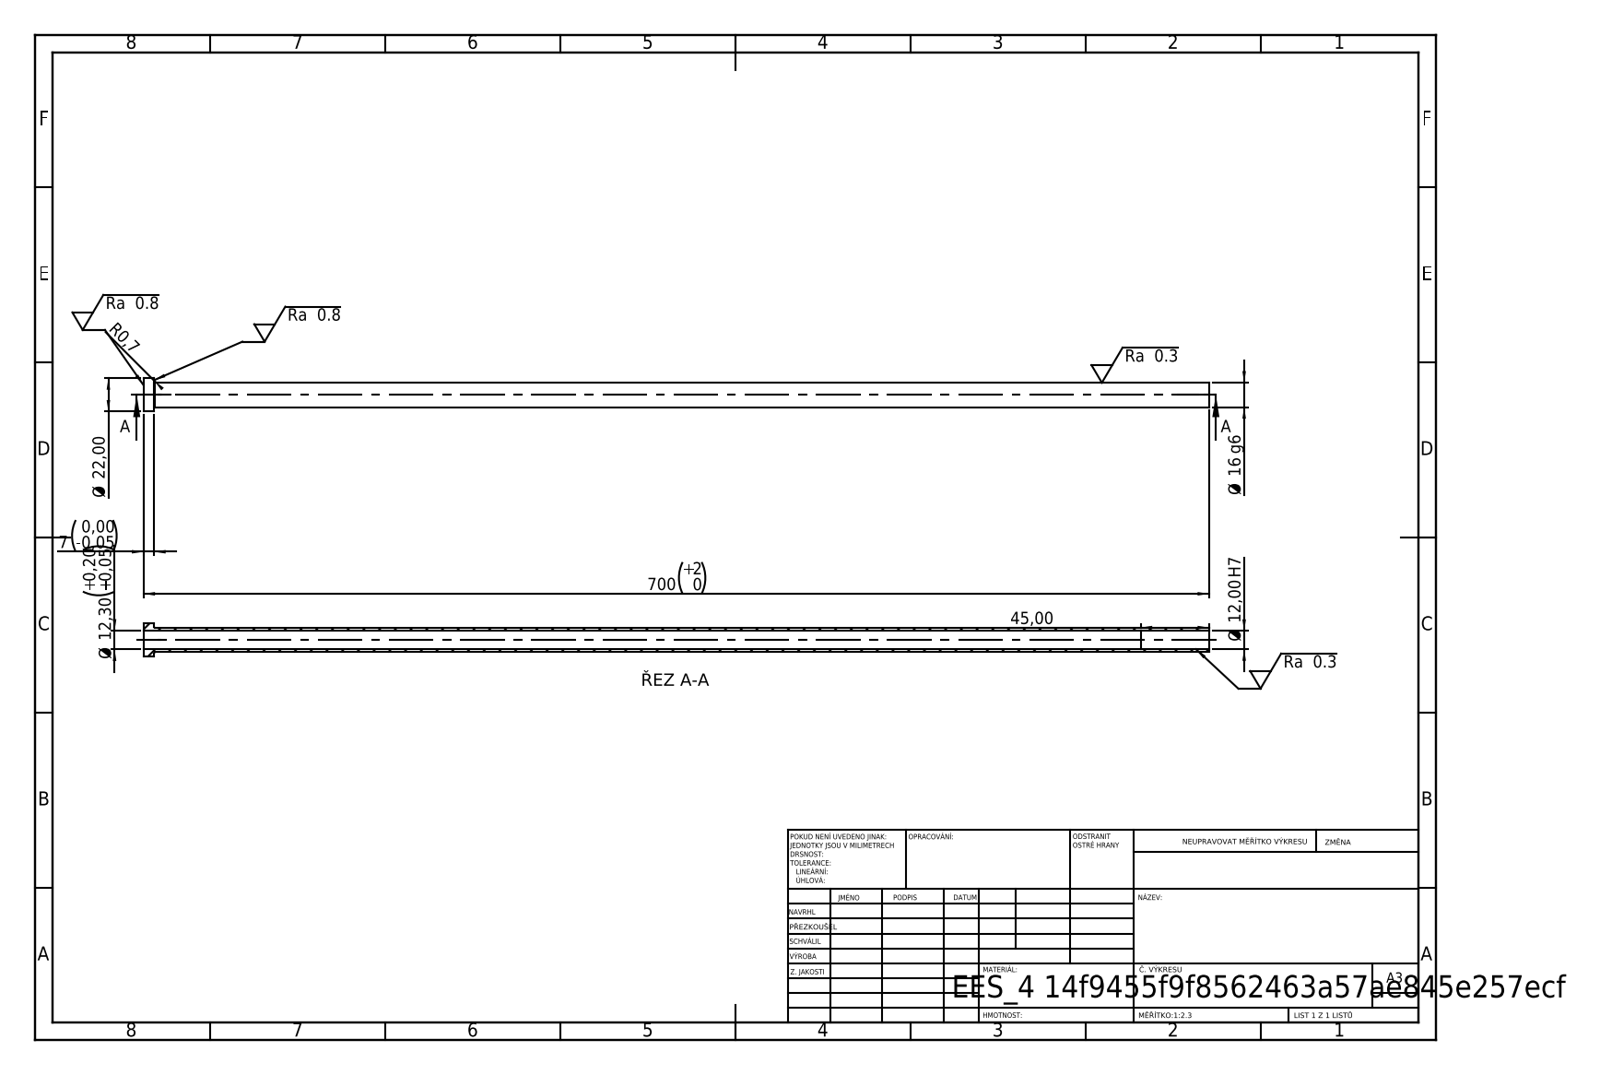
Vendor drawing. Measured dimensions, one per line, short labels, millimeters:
written by: SolidWorks 2019 (CONFIG_CONTROL_DESIGN)
unit: mm
bodies: 1 solid, 14 faces (4 planar, 8 cylindrical, 2 other)
size: 700 × 22 × 22
volume: 59 084 mm³; area: 62 844 mm²
holes: 1× ⌀12, 1× ⌀12.3
bosses: 1× ⌀22, 1× ⌀16
face distances: 7, 700, 693, 655, 648, 45
